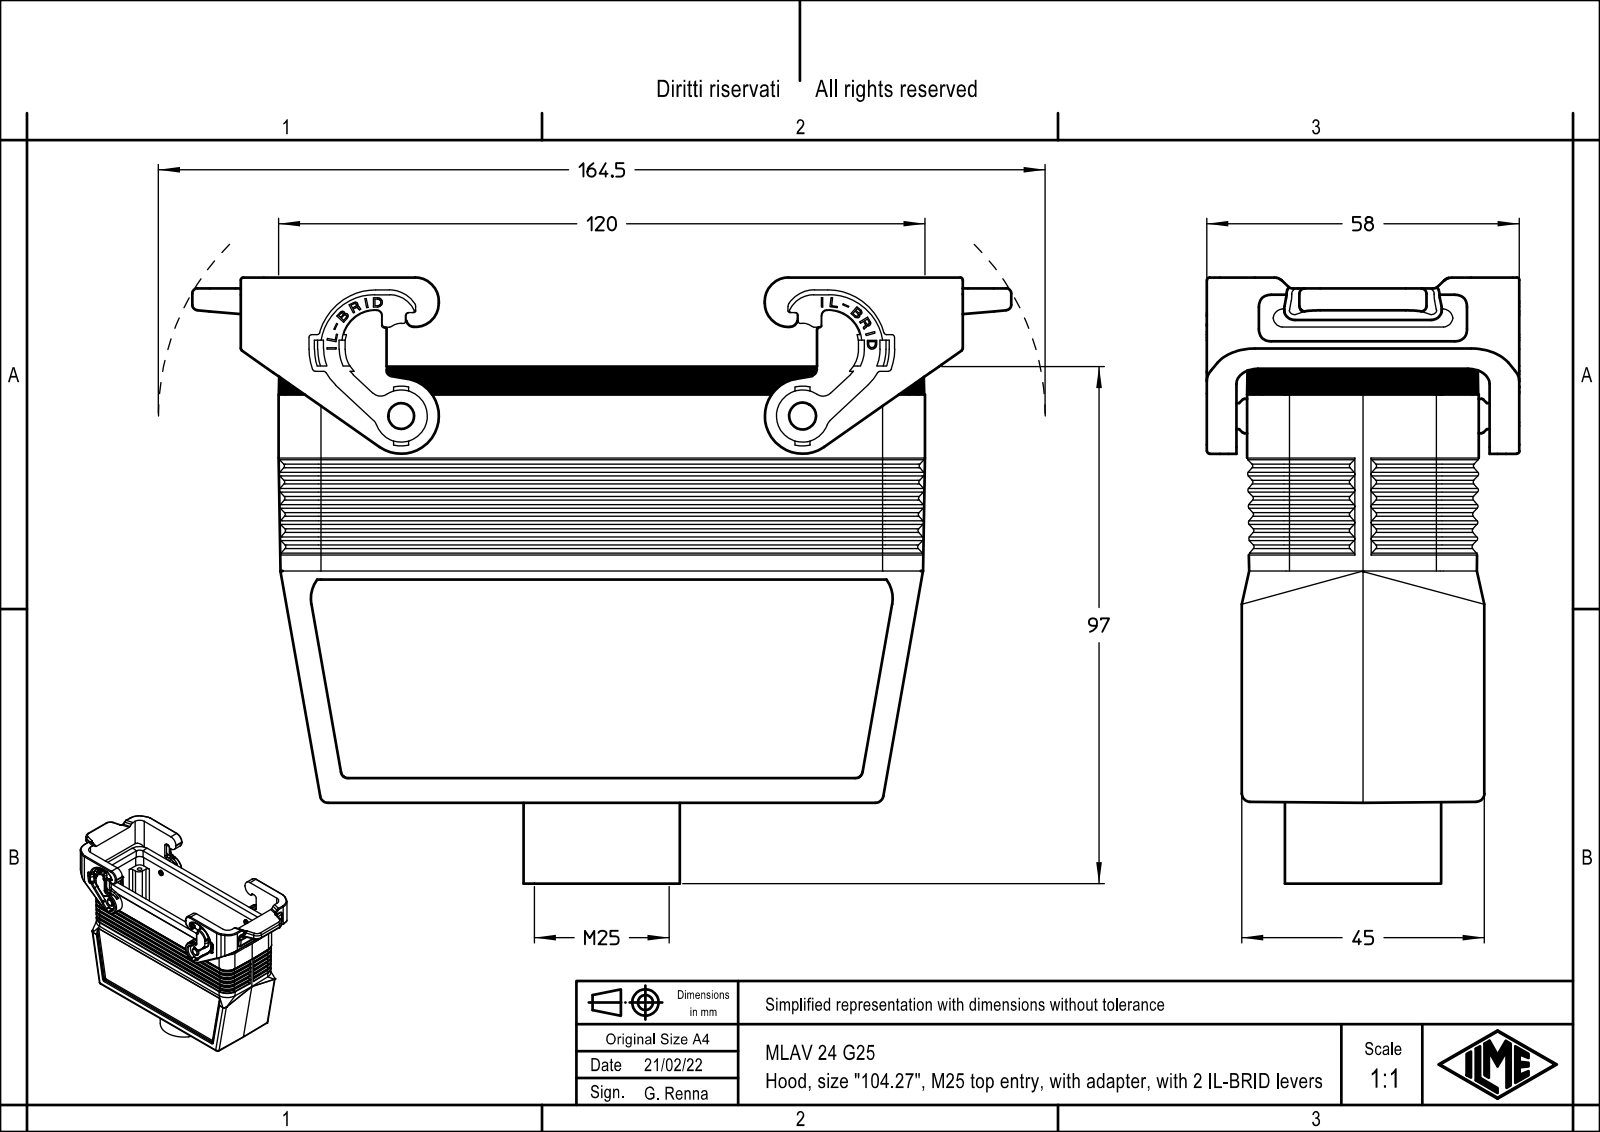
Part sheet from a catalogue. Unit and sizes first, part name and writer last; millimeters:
Units: millimetres
Overall size (bounding box): 152 × 112.45 × 58
Round holes (diameter × count): ⌀2.75 ×4, ⌀20 ×1, ⌀25 ×1
Round bosses / shafts (diameter × count): ⌀6.8 ×2, ⌀4.8 ×2, ⌀29 ×1
Partial cylindrical surfaces — rounded edges, fillets, slot ends (radius × count): R0.5 ×104, R1 ×46, R3 ×20, R7 ×16, R0.33 ×15, R1.5 ×14, R0.3 ×8, R2 ×8
Main face-to-face distances: 39.25, 3.75, 2, 1, 4.75, 43, 5.75, 34.5, 38.25, 35.5
Hole centre spacings: 53.72, 27, 104, 107.45
Volume: 143 358 mm³ · Surface area: 75 031 mm²
Bodies: 1 solid, 1612 faces (1031 planar, 395 cylindrical, 186 other)
Part name (STEP PRODUCT): MLAV_24_G25
STEP written by: Creo Elements/Direct Modeling 20.1B 02-Apr-2019 (C) Parametric Technology GmbH (AUTOMOTIVE_DESIGN)
